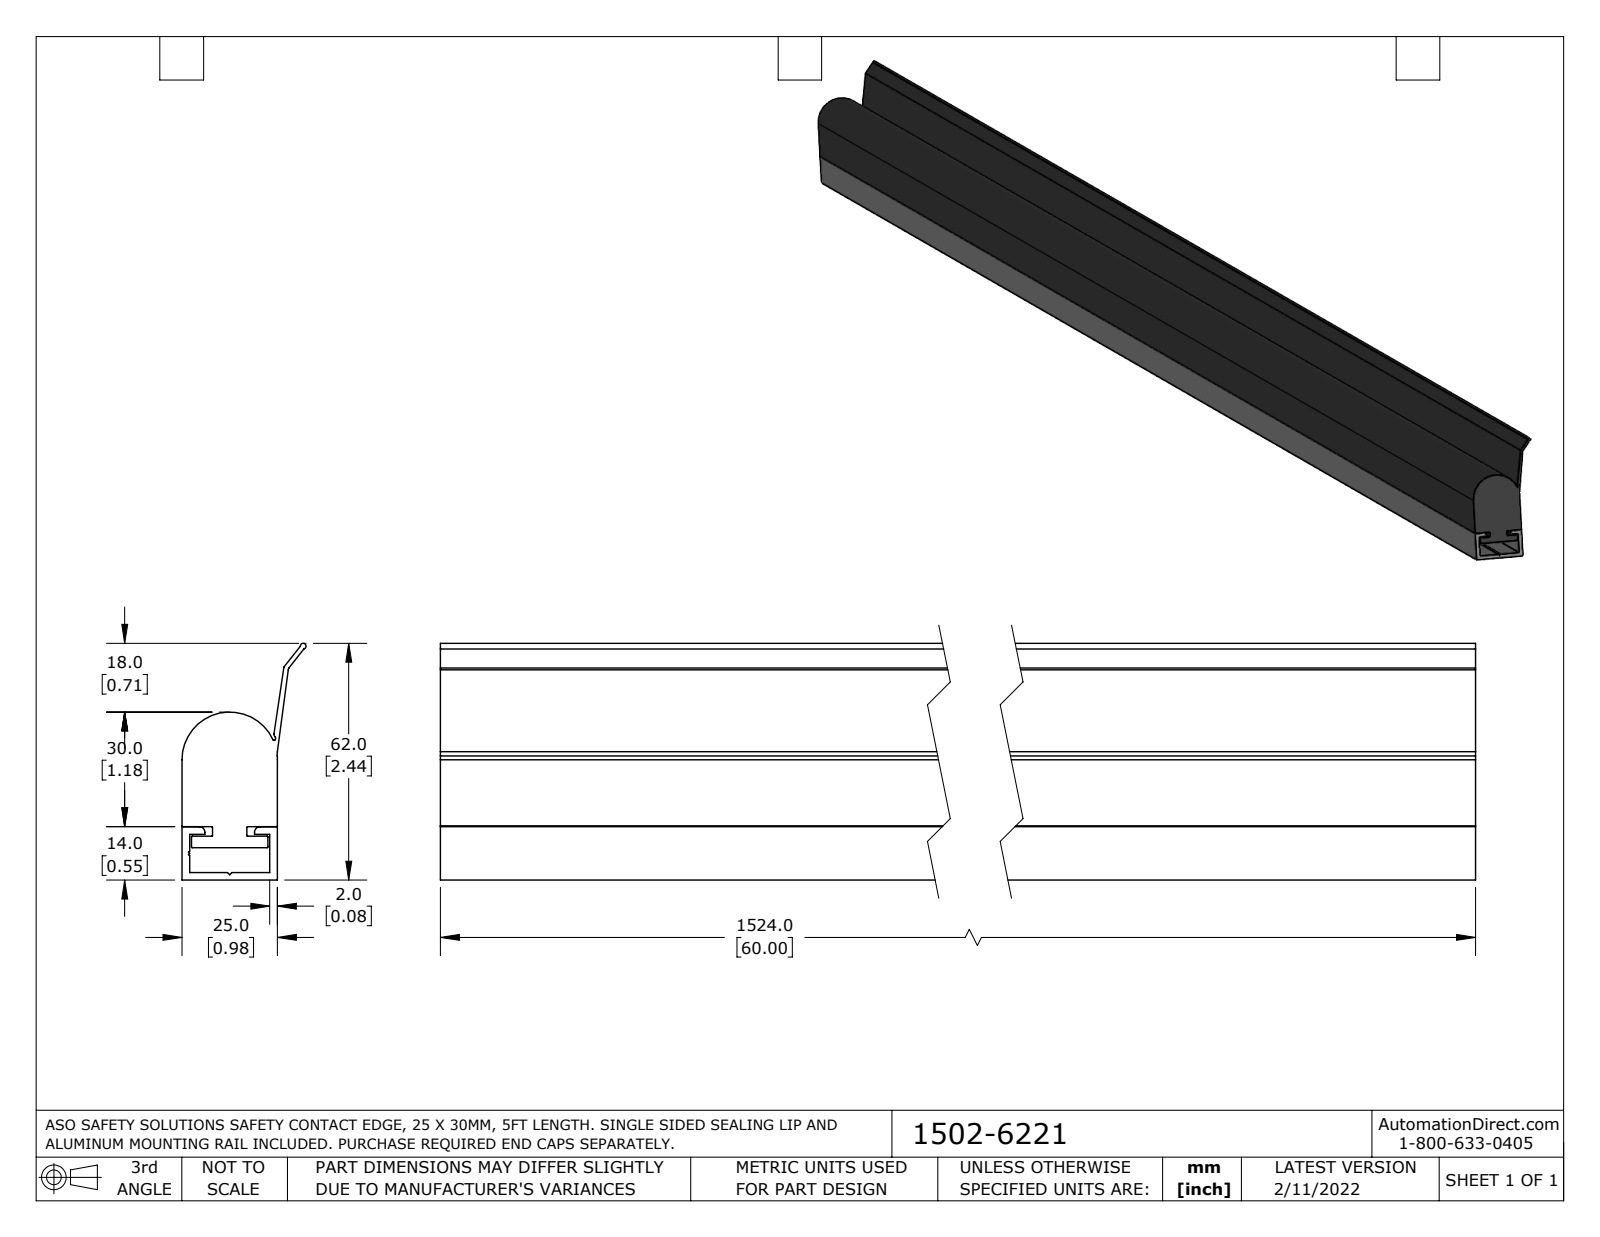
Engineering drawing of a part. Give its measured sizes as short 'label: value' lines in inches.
name: 1502-6221
written by: SolidWorks 2021 (AUTOMOTIVE_DESIGN)
unit: in
bodies: 2 solids, 62 faces (39 planar, 23 cylindrical, 0 other)
size: 60 × 2.441 × 1.28
volume: 85.11 in³; area: 722.6 in²
rounds: 10× R0.008, 2× R0.024, 2× R0.059, 1× R0.012, 1× R0.03, 1× R0.031, 1× R0.039, 1× R0.197
face distances: 0.079, 0.984, 0.472, 0.551, 0.217, 0.335, 0.256, 0.906, 0.098, 0.02
